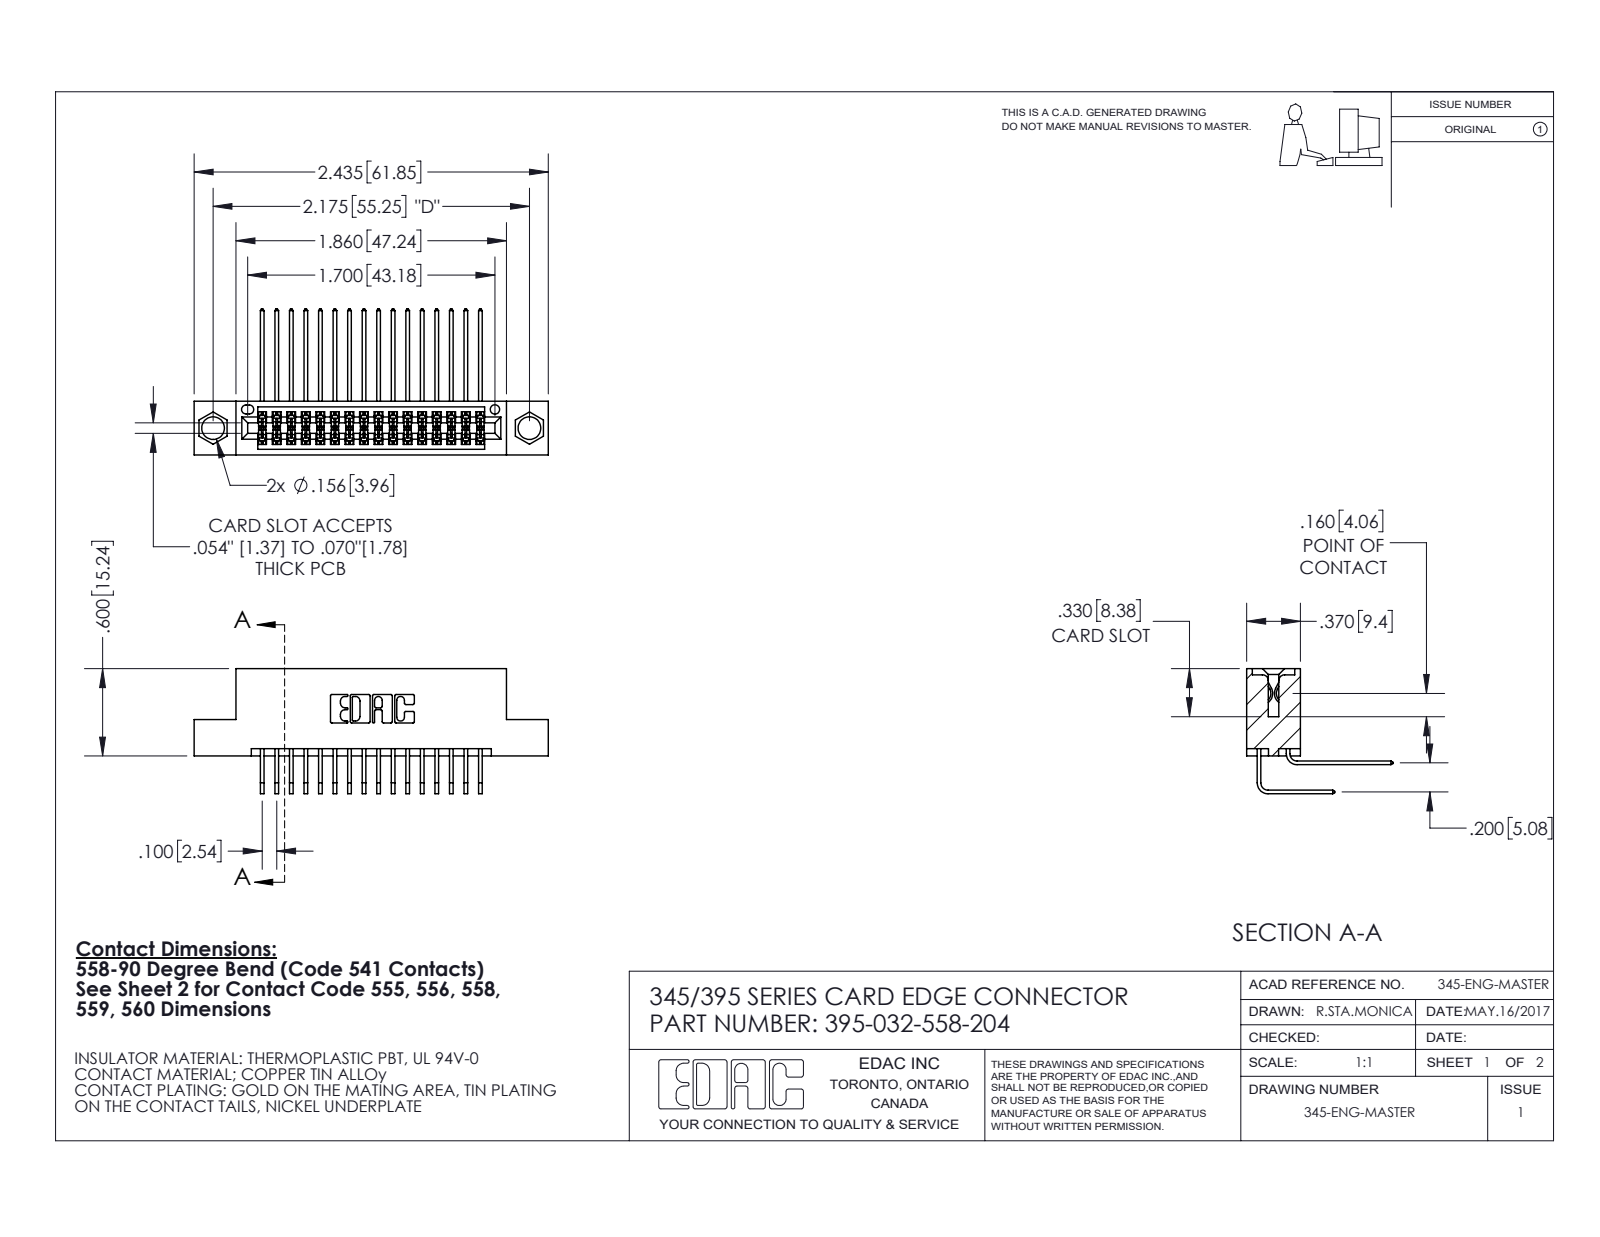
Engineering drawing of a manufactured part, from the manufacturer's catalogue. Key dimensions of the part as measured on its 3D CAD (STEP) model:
Part name (STEP PRODUCT): 345 Part_Flush Mounting Lugs - 0.156 Dia-TI; 345-292-001_558 559 Tail - 1; 345-292-001_558 Tail - 2; 395-032-558-204
STEP written by: SolidWorks 2020 (CONFIG_CONTROL_DESIGN)
Units: inches
Bodies: 33 solids, 1804 faces (1214 planar, 590 cylindrical, 0 other)
Overall size (bounding box): 2.435 × 1.005 × 0.859
Volume: 0.357 in³ · Surface area: 13.73 in²
Round holes (diameter × count): ⌀0.156 ×2, ⌀0.064 ×1
Partial cylindrical surfaces — rounded edges, fillets, slot ends (radius × count): R0.006 ×64, R0.01 ×22, R0.007 ×6, R0.031 ×6, R0.026 ×3, R0.014 ×2, R0.019 ×2, R0.022 ×2
Main face-to-face distances: 0.2, 0.072, 0.298, 0.37, 0.098, 0.272, 0.025, 0.225, 0.285, 0.1
Hole centre spacings: 0.27, 1.942, 2.175
